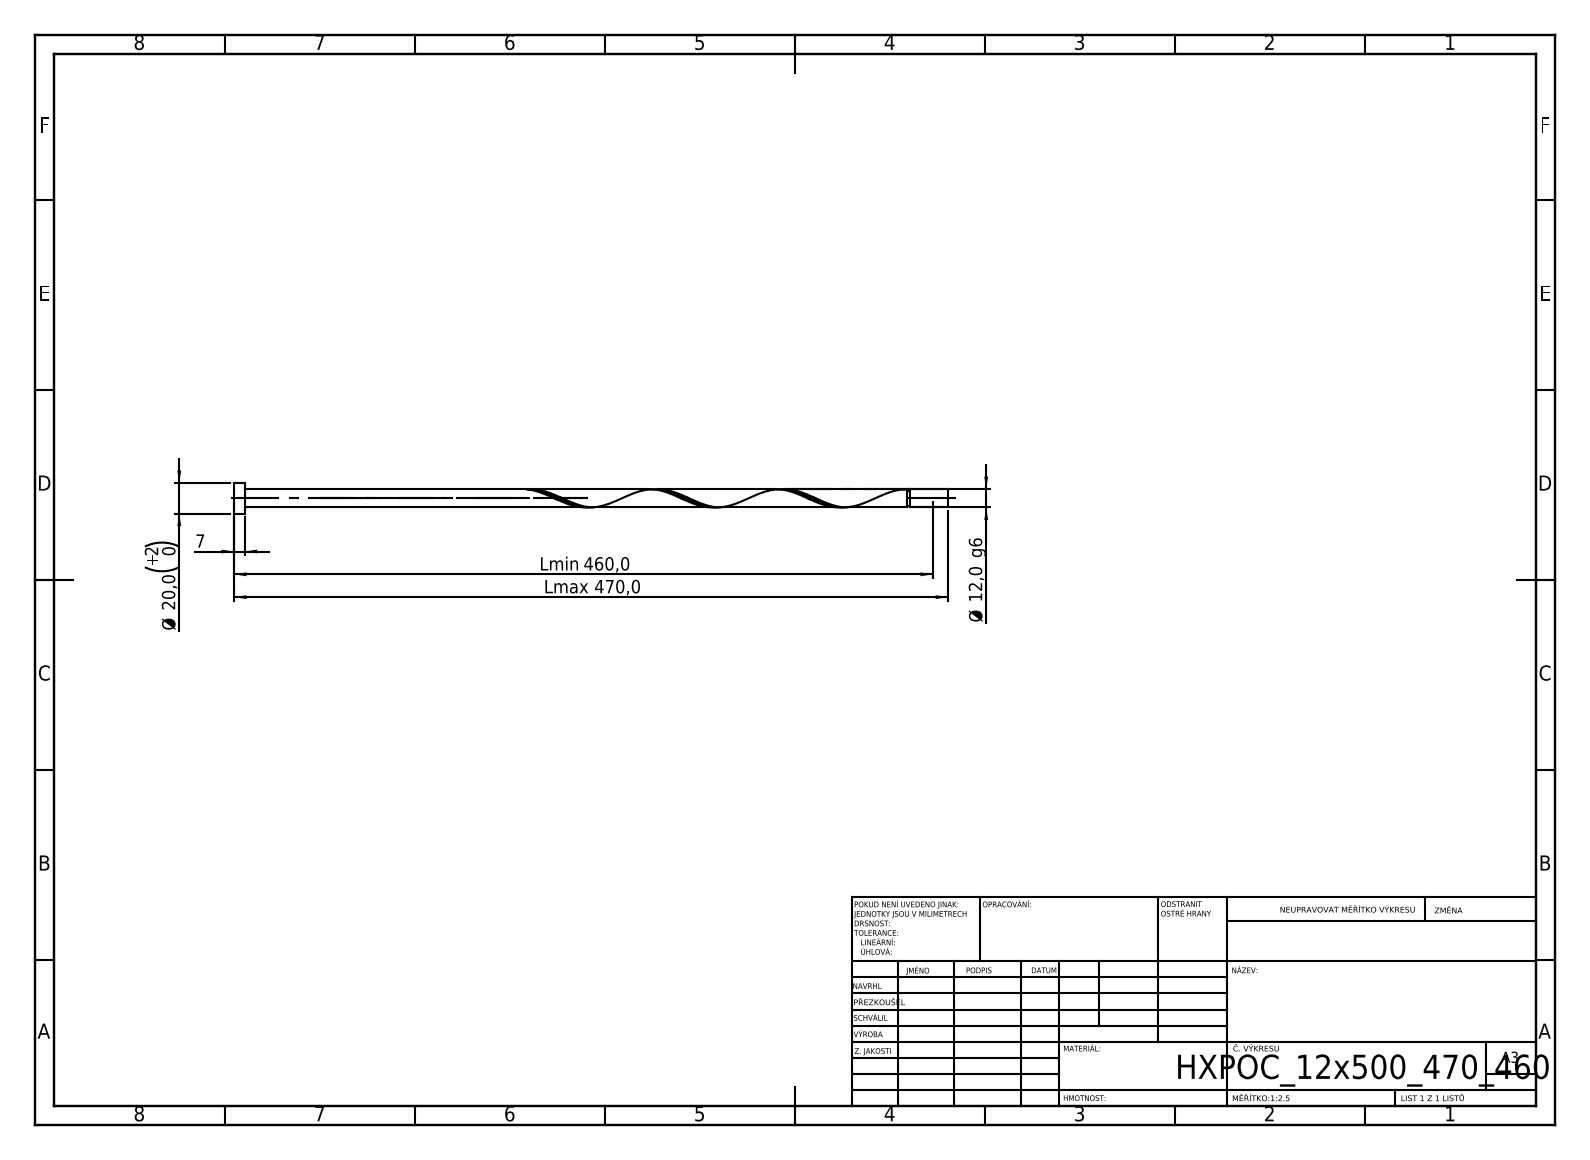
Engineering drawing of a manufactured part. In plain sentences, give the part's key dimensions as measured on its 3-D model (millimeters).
Its 3-D file was written by "SolidWorks 2019 (CONFIG_CONTROL_DESIGN)". It is 1 solid with 21 faces: 6 planar, 14 cylindrical and 1 other. Overall it measures 470 by 20 by 20 millimeters. Its volume is 53 924 cubic millimeters and its surface area 18 908 square millimeters. Round bosses or shafts: 1 of diameter 20, 1 of diameter 12, 1 of diameter 9.6. The main face-to-face distances are 7, 470, 463, 445.11, 438.11, 24.89, 442.71, 435.71, 2.4, 27.29.
